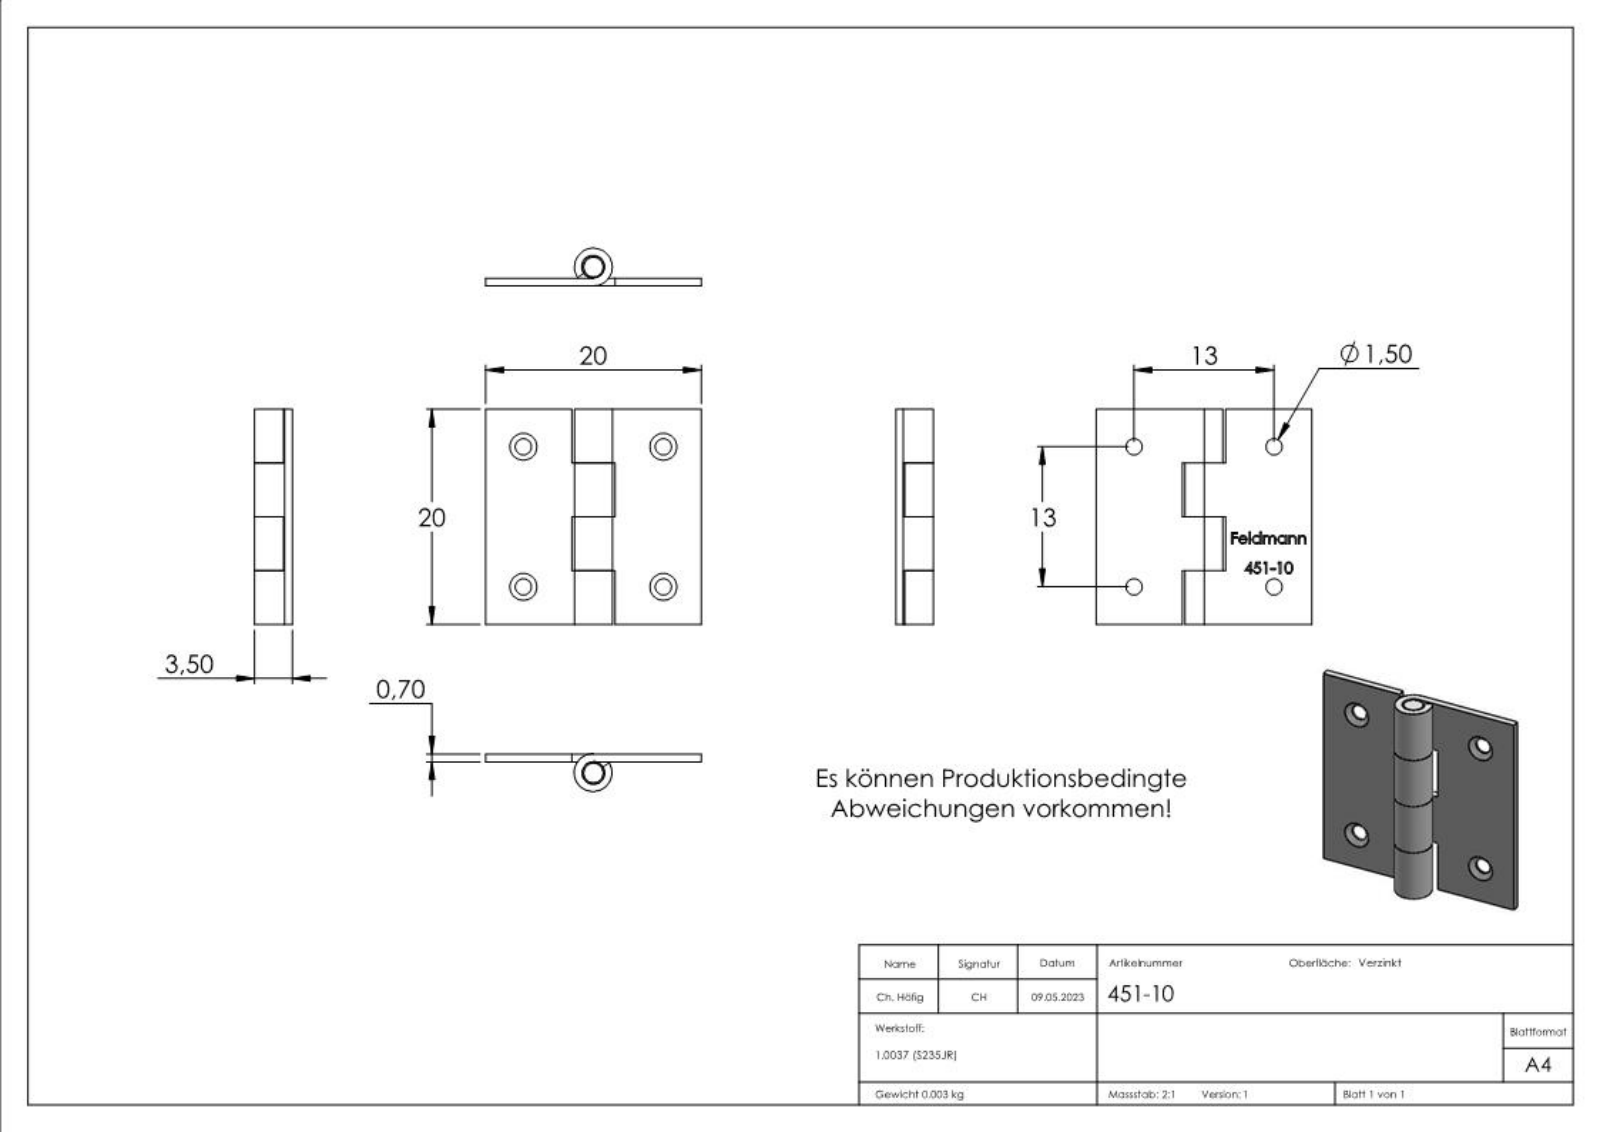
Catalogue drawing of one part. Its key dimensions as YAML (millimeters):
part_name: "451-10 Teil2; 451-10; 451-10 Teil3; 451-10 Teil1"
step_written_by: "SolidWorks 2018 (CONFIG_CONTROL_DESIGN)"
units: millimeters
bodies: {solids: 3, faces: 218, planar: 134, cylindrical: 13, other: 71}
overall_size: [20, 20, 3.5]
volume: 410
surface_area: 1273
round_holes:
  - {diameter: 1.5, count: 4}
  - {diameter: 2.1, count: 1}
round_bosses_or_shafts:
  - {diameter: 3.5, count: 1}
  - {diameter: 2, count: 1}
face_to_face_distances: [0.7, 5, 10, 20, 15, 8, 12, 4, 19.95, 4.95]
hole_center_spacings: [13, 18.38]
